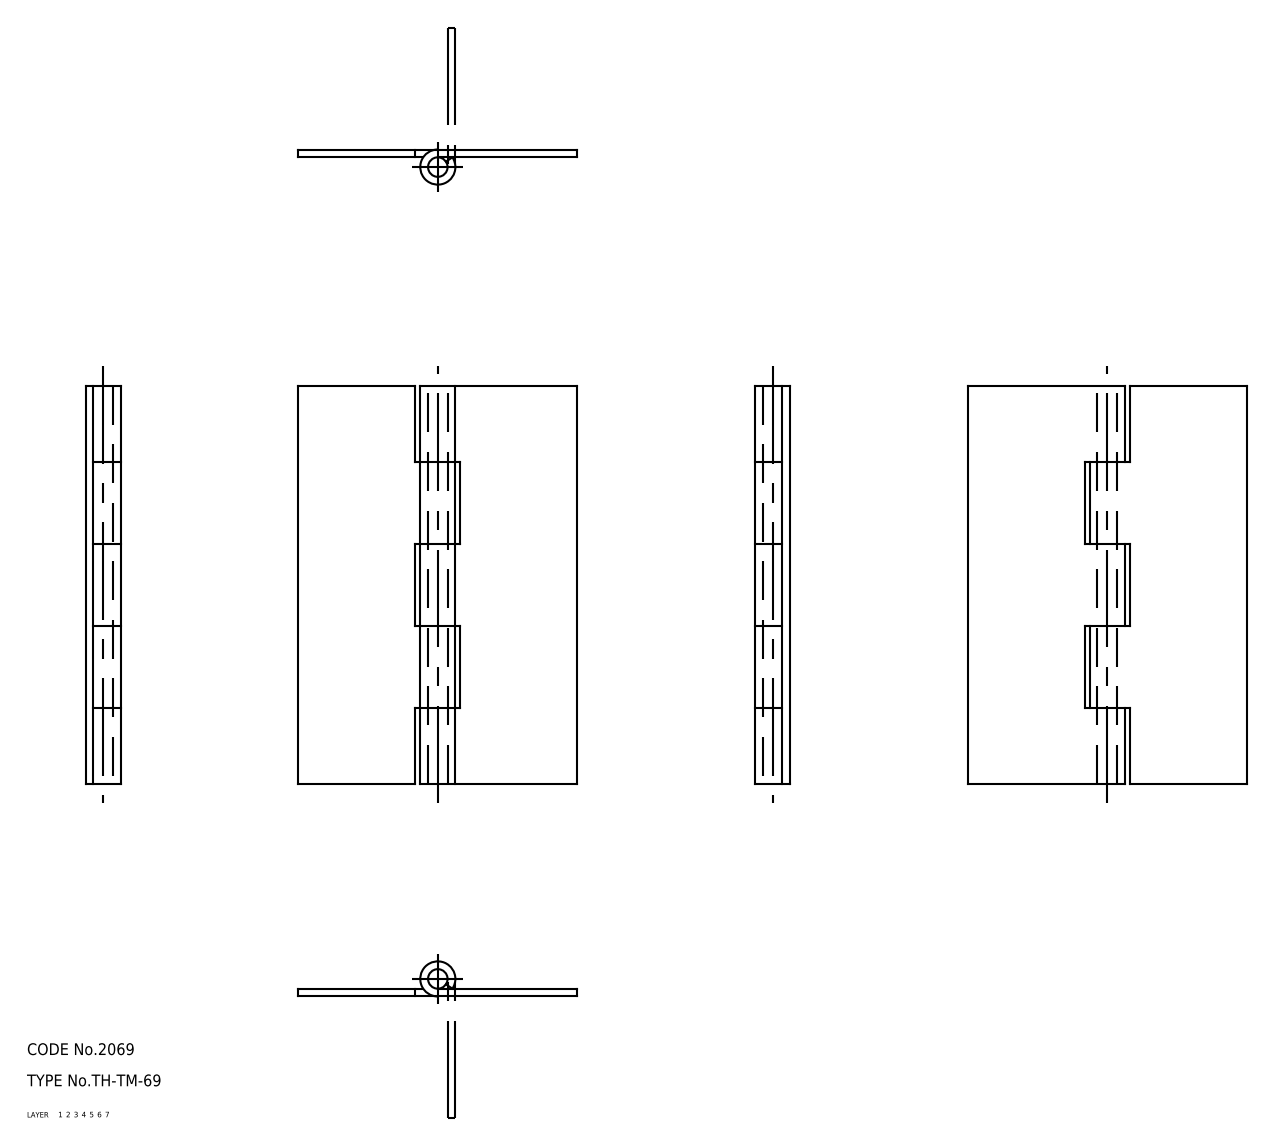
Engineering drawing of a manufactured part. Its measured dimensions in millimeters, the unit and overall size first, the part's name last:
Units: millimetres
Overall size (bounding box): 102 × 71.5 × 9
Volume: 19 195 mm³ · Surface area: 20 373 mm²
Bodies: 3 solids, 42 faces (0 planar, 0 cylindrical, 42 other)
Part name (STEP PRODUCT): hinge piece_B; hinge piece_A; shaft; TH_TM_69_24991_36
STEP written by: CADfix (AUTOMOTIVE_DESIGN)
